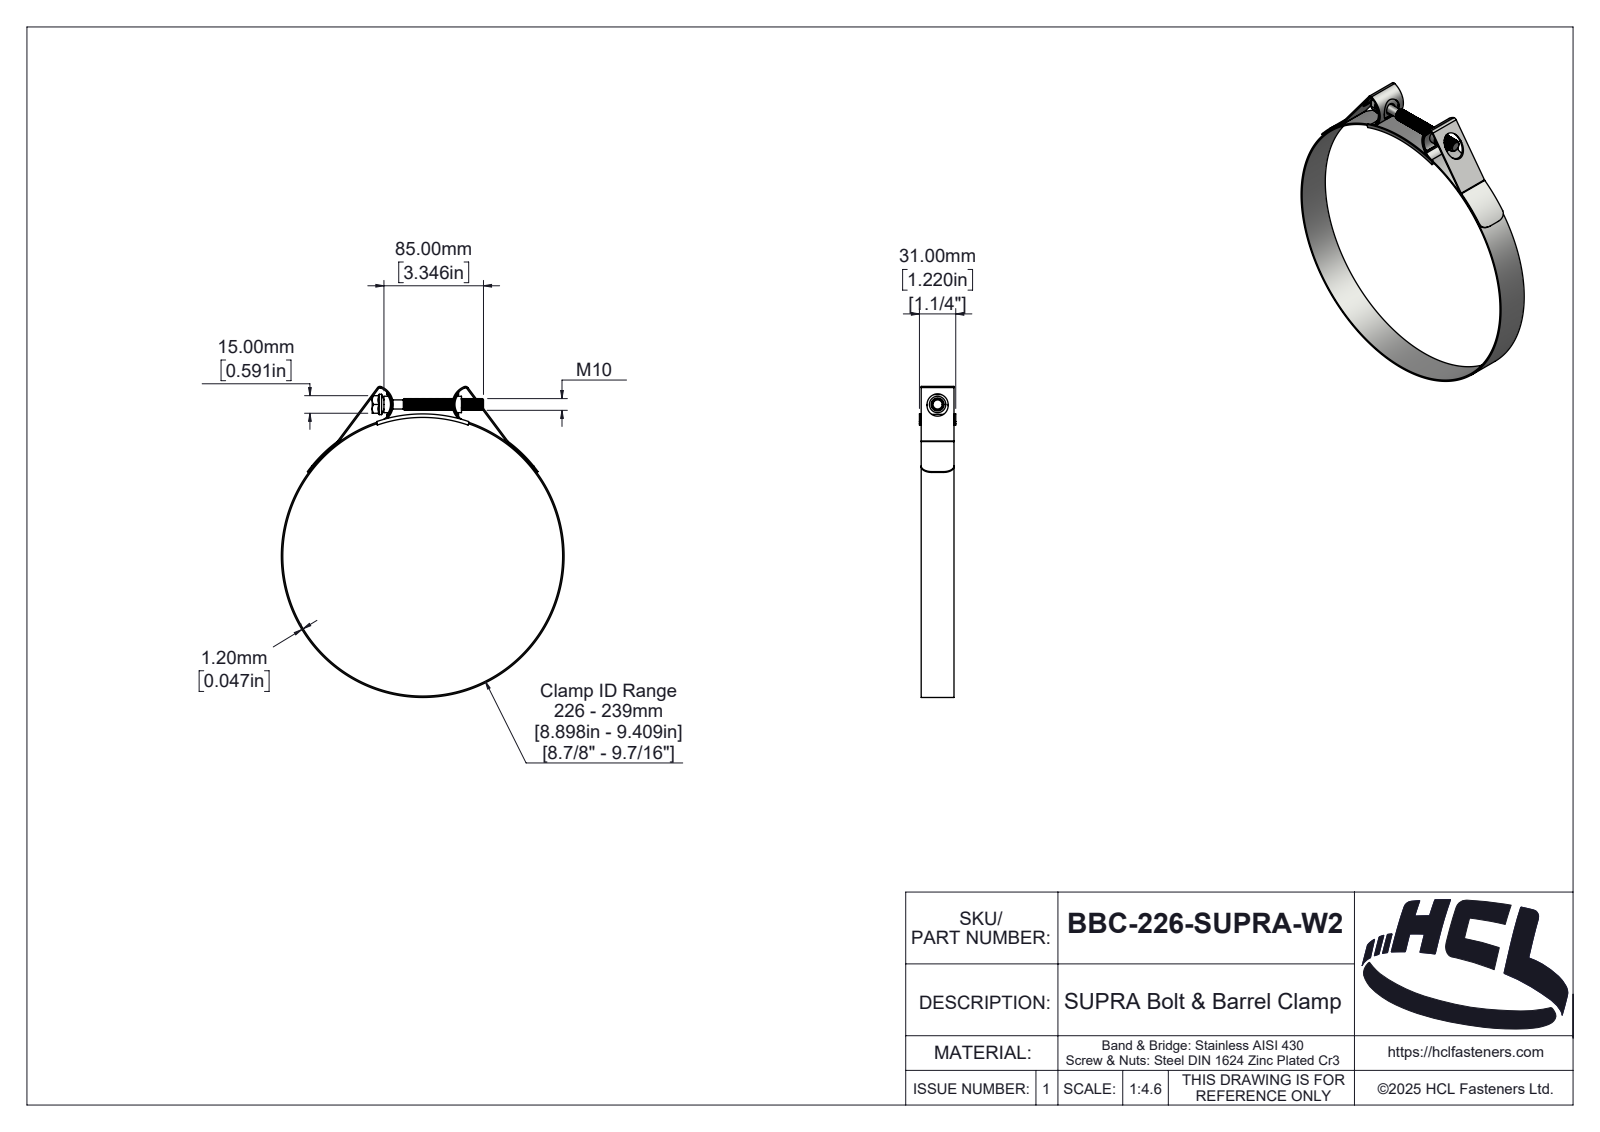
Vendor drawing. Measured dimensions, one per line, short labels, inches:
name: BBC-226-SUPRA-W2
written by: SolidWorks 2025 (AUTOMOTIVE_DESIGN)
unit: in
bodies: 5 solids, 381 faces (50 planar, 245 cylindrical, 86 other)
size: 10.452 × 9.504 × 1.22
volume: 2.62 in³; area: 103.3 in²
holes: 1× ⌀9.409
bosses: 1× ⌀9.504, 1× ⌀0.682, 1× ⌀0.551, 1× ⌀0.394, 1× ⌀0.307
rounds: 4× R0.039, 2× R0.051, 2× R0.079, 2× R0.098, 2× R0.126, 2× R0.354, 2× R0.554, 2× R0.593
face distances: 0.047, 1.102, 0.059, 1.161, 1.173, 1.114, 1.22, 1.126, 0.591, 0.098
